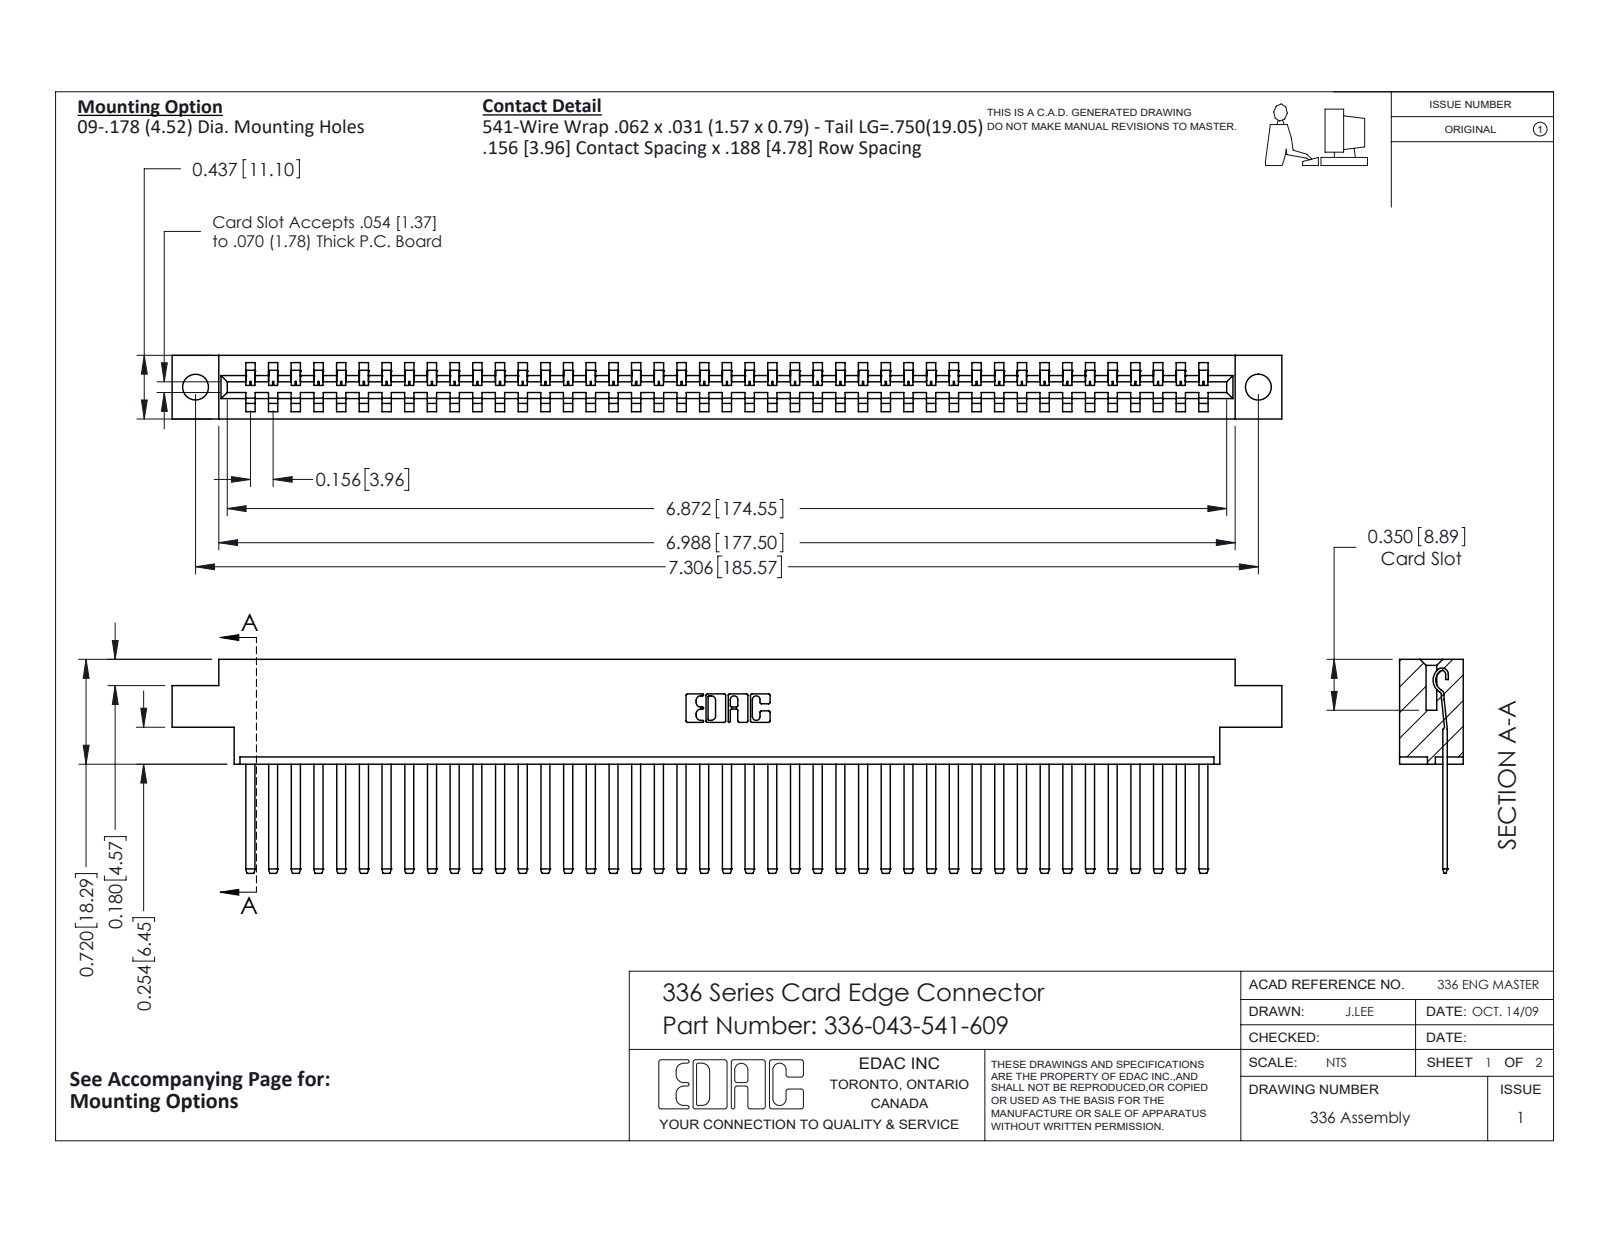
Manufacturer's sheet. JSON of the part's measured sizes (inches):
{"part_name": "336-043-541-609; 336 Part_Offset - .178 Dia - TH; 336-290-001_336-290-541", "step_written_by": "SolidWorks 2020 (CONFIG_CONTROL_DESIGN)", "units": "inches", "bodies": {"solids": 44, "faces": 2268, "planar": 1536, "cylindrical": 732, "other": 0}, "overall_size": [7.629, 1.47, 0.437], "volume_in3": 1.716, "surface_area_in2": 47.38, "round_holes": [[0.178, 2]], "partial_cylinders_radius": [[0.004, 86], [0.056, 86], [0.01, 22], [0.007, 6], [0.031, 6], [0.026, 3], [0.022, 2], [0.04, 2]], "face_to_face_distances": [0.437, 0.181, 0.328, 0.14, 0.297, 0.109, 0.031, 0.256, 0.05, 0.387], "hole_center_spacings": [7.306]}
